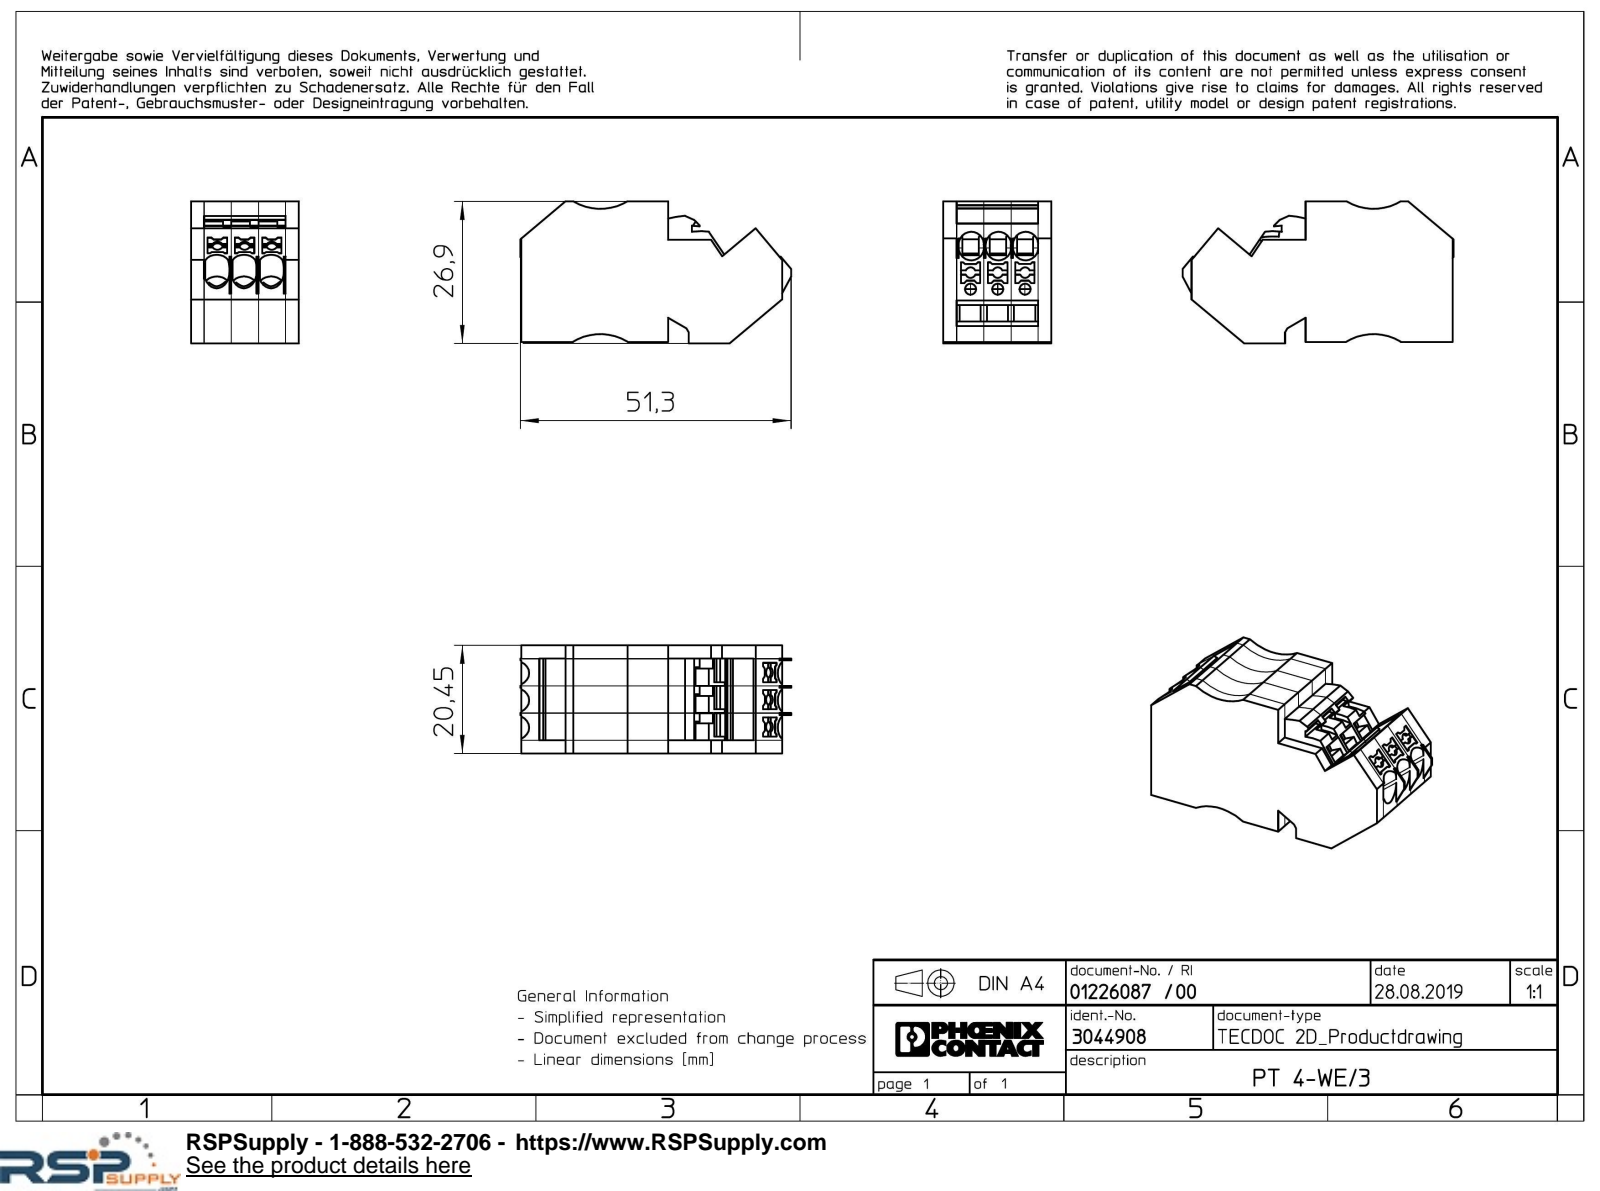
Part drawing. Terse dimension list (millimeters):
name: PT_4_WE_3-select
written by: Creo Elements/Direct Modeling 20.1A 29-Sep-2018 (C) Parametric Technology GmbH (AUTOMOTIVE_DESIGN)
unit: mm
bodies: 1 solid, 543 faces (473 planar, 64 cylindrical, 6 other)
size: 51.3 × 26.9 × 20.45
volume: 19 002 mm³; area: 8 115 mm²
holes: 3× ⌀2.1
rounds: 12× R2.4, 6× R1, 3× R1.03, 2× R10, 1× R1.05, 1× R1.78, 1× R12.4, 1× R13.38
face distances: 20.45, 5.15, 10.3, 19.6, 3.15, 3.85, 7, 7.3, 26.6, 22.75
hole spacings: 5.15, 10.3
